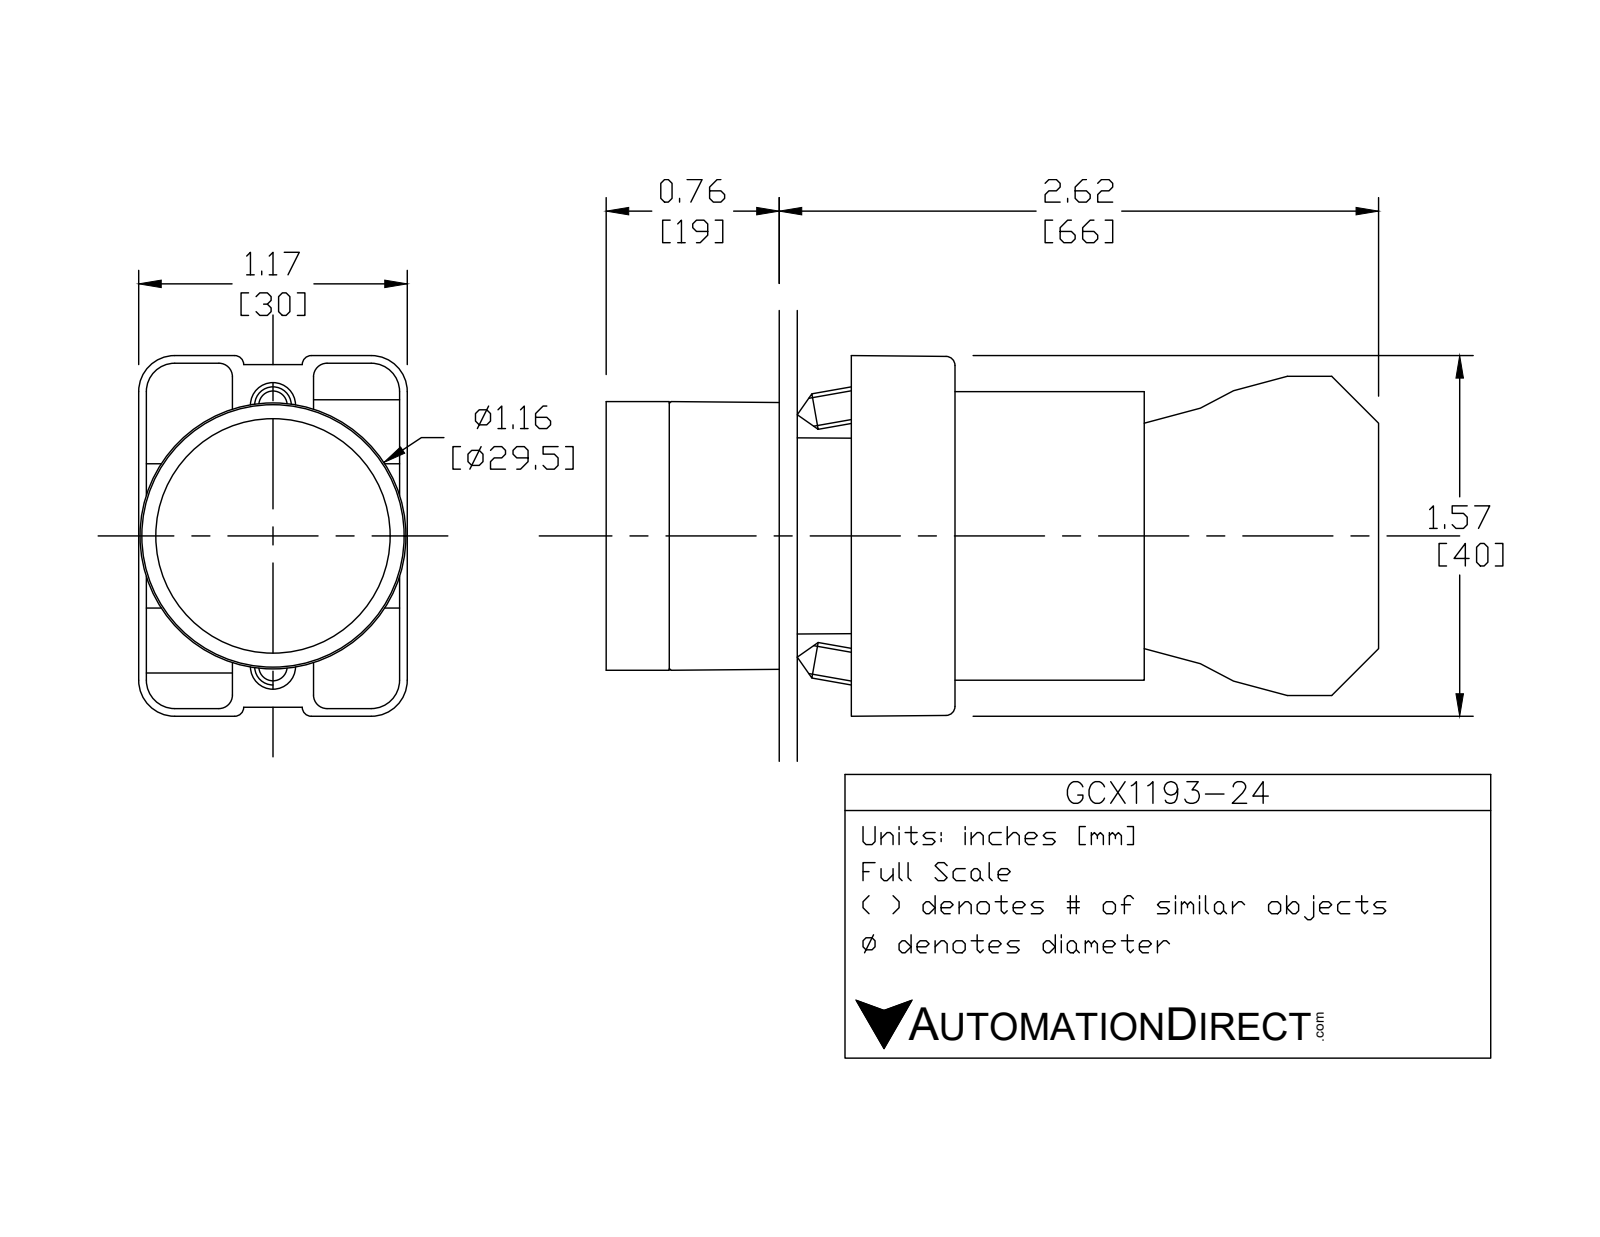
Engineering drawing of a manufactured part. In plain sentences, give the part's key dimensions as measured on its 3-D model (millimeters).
The part is named "GCX1193 OPERATOR; GCX1193-24; ECX1050; ecx1040 (+1 more)". Its 3-D file was written by "SolidWorks 2016 (AUTOMOTIVE_DESIGN)". It is 8 solids with 431 faces: 252 planar, 148 cylindrical and 31 other. Overall it measures 84.3 by 40.2 by 29.9 millimeters. Its volume is 45 790 cubic millimeters and its surface area 25 000 square millimeters. Round holes: 2 of diameter 2, 2 of diameter 3.1, 2 of diameter 3.3, 1 of diameter 2.2, 1 of diameter 5, 1 of diameter 11.9, 1 of diameter 22.3, 1 of diameter 22.6, 1 of diameter 26. Round bosses or shafts: 4 of diameter 4, 1 of diameter 29.8, 1 of diameter 25.5, 1 of diameter 24, 1 of diameter 21.7, 1 of diameter 19.8, 1 of diameter 12.8. Partial cylindrical surfaces (rounded edges, fillets, slot ends): 24 of radius 1.5, 12 of radius 1, 12 of radius 3.1, 12 of radius 4, 8 of radius 1, 2 of radius 3.3, 1 of radius 0.5, 1 of radius 1.6. The main face-to-face distances are 21, 51.3, 30.3, 14.7, 29.7, 0.8, 7, 0.8, 19, 14.6. The hole center spacings are 6, 13.8, 12, 12.4.
